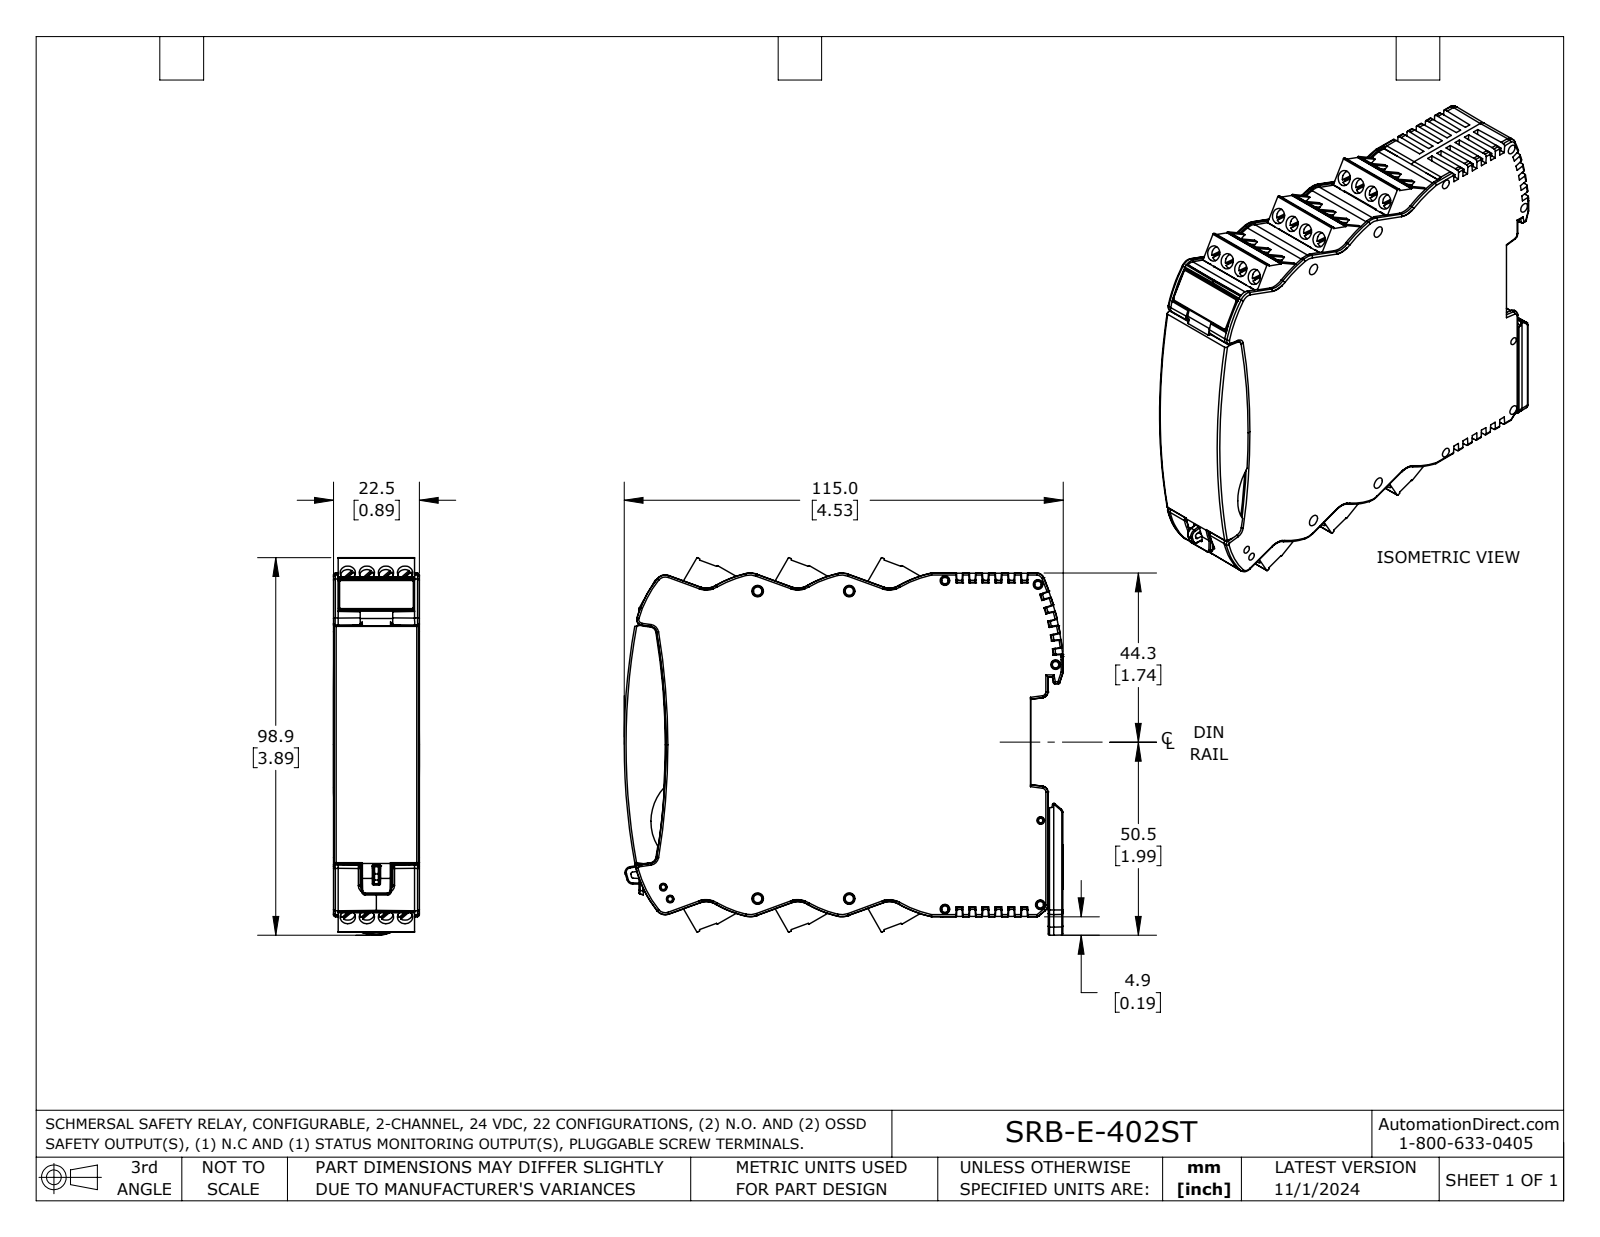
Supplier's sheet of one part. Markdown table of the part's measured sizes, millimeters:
| quantity | value |
| --- | --- |
| part name | SRB-E-402ST |
| STEP written by | SolidWorks 2023 (AUTOMOTIVE_DESIGN) |
| units | millimeters |
| bodies | 2 solids, 3031 faces (1677 planar, 698 cylindrical, 656 other) |
| overall size | 115 × 98.9 × 22.5 |
| volume | 213 500 mm³ |
| surface area | 42 020 mm² |
| round holes (diameter × count) | 4 × 24 |
| round bosses / shafts (diameter × count) | 3.8 × 24, 1.7 × 1 |
| partial cylindrical surfaces (radius × count) | 0.3 × 175, 0.5 × 117, 0.2 × 39, 0.3 × 36, 1.5 × 26, 1 × 16, 0.2 × 10, 2 × 8 |
| main face-to-face distances | 22.5, 1.2, 21.3, 3.4, 6.8, 0.9, 3.4, 0.4, 21.6, 20.3 |
| hole center spacings | 5, 10, 13, 13.2, 24.7, 12, 12.2, 15.6 |
